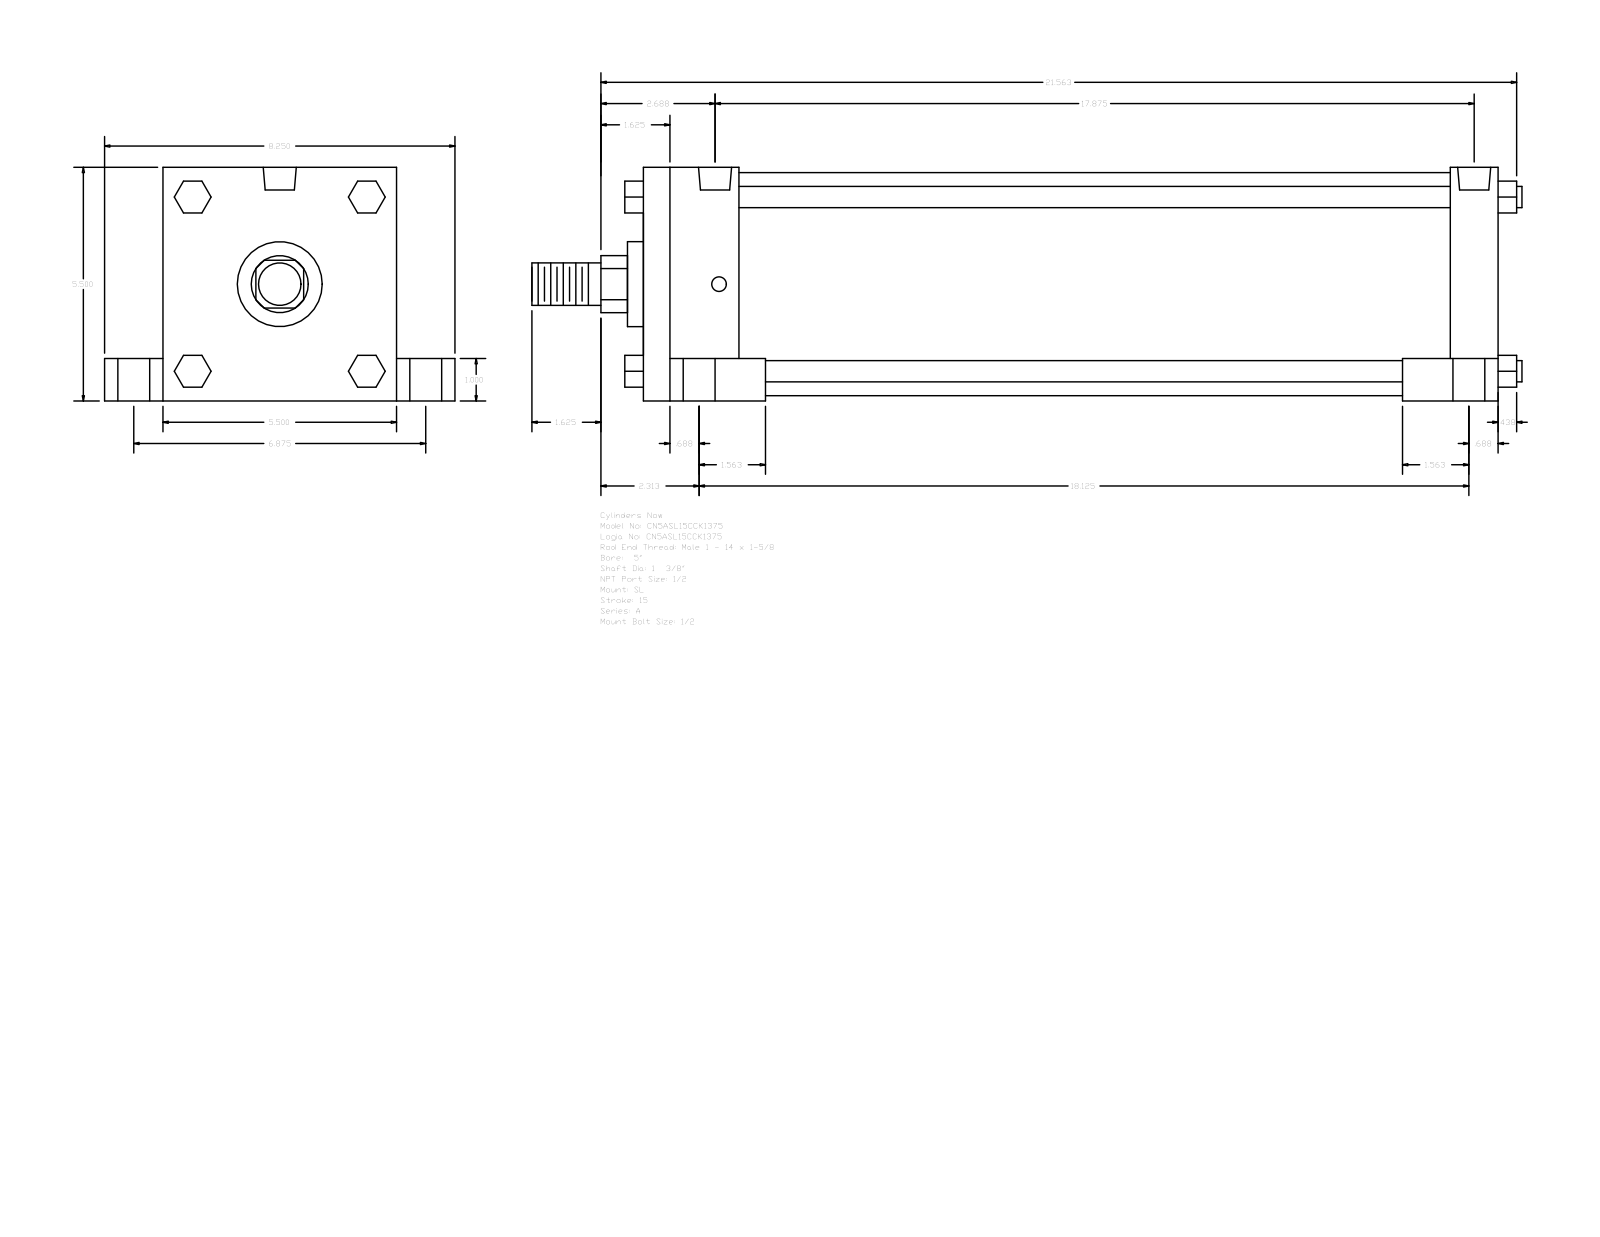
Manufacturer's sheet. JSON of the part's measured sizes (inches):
{"part_name": "A_SL__0500_1.375", "step_written_by": "GSSL Pune (CONFIG_CONTROL_DESIGN)", "units": "inches", "bodies": {"solids": 0, "faces": 150, "planar": 114, "cylindrical": 36, "other": 0}, "overall_size": [23.313, 8.25, 5.5], "round_holes": [[0.344, 4], [0.75, 4], [1, 4], [0.778, 2]], "round_bosses_or_shafts": [[0.5, 4], [5.25, 1], [2, 1], [1.375, 1], [1, 1]], "partial_cylinders_radius": [[0.672, 1]], "face_to_face_distances": [5.5, 20.125, 2.25, 17.875, 1, 4.5, 1.375, 6.875, 1.125, 19], "hole_center_spacings": [0.094, 3.437, 3.44, 3.458, 3.469, 6.875, 17.687, 17.781]}
